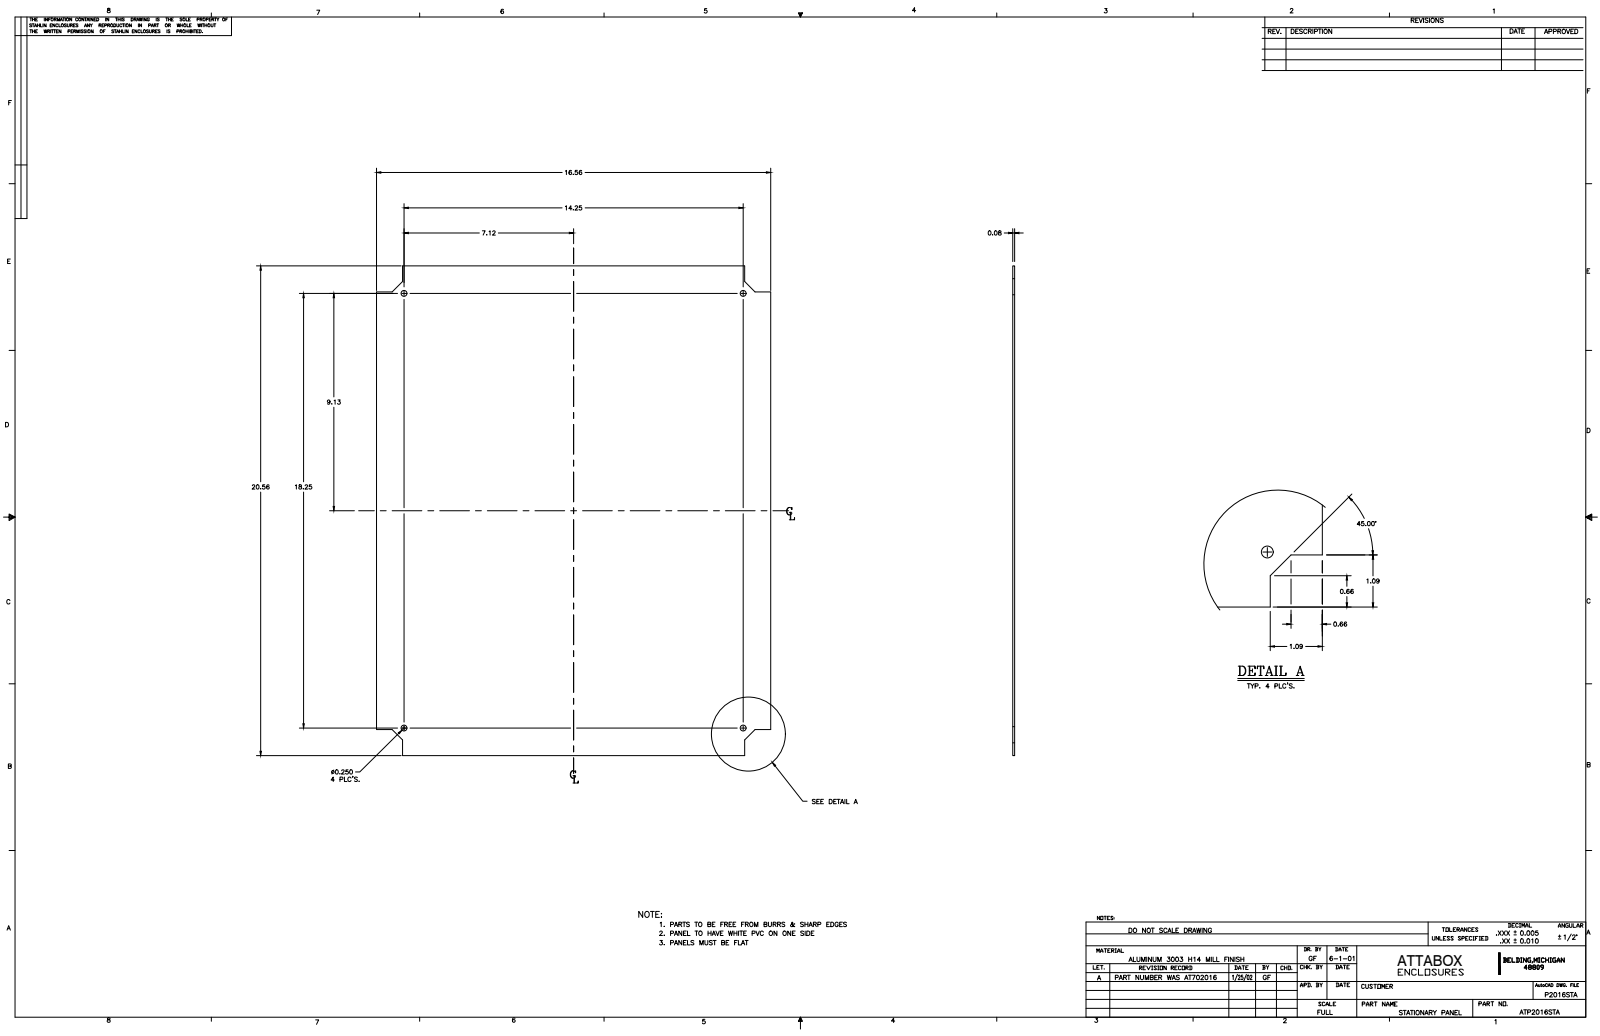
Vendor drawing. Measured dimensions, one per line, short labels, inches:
name: P2016STAL
written by: Autodesk Inventor 11 (AUTOMOTIVE_DESIGN)
unit: in
bodies: 1 solid, 22 faces (18 planar, 4 cylindrical, 0 other)
size: 20.563 × 16.563 × 0.08
volume: 26.88 in³; area: 678 in²
holes: 4× ⌀0.25
face distances: 0.08, 16.562, 20.562, 1.094, 15.468, 19.468, 14.374, 18.374, 23.771
hole spacings: 14.25, 18.25, 23.154
